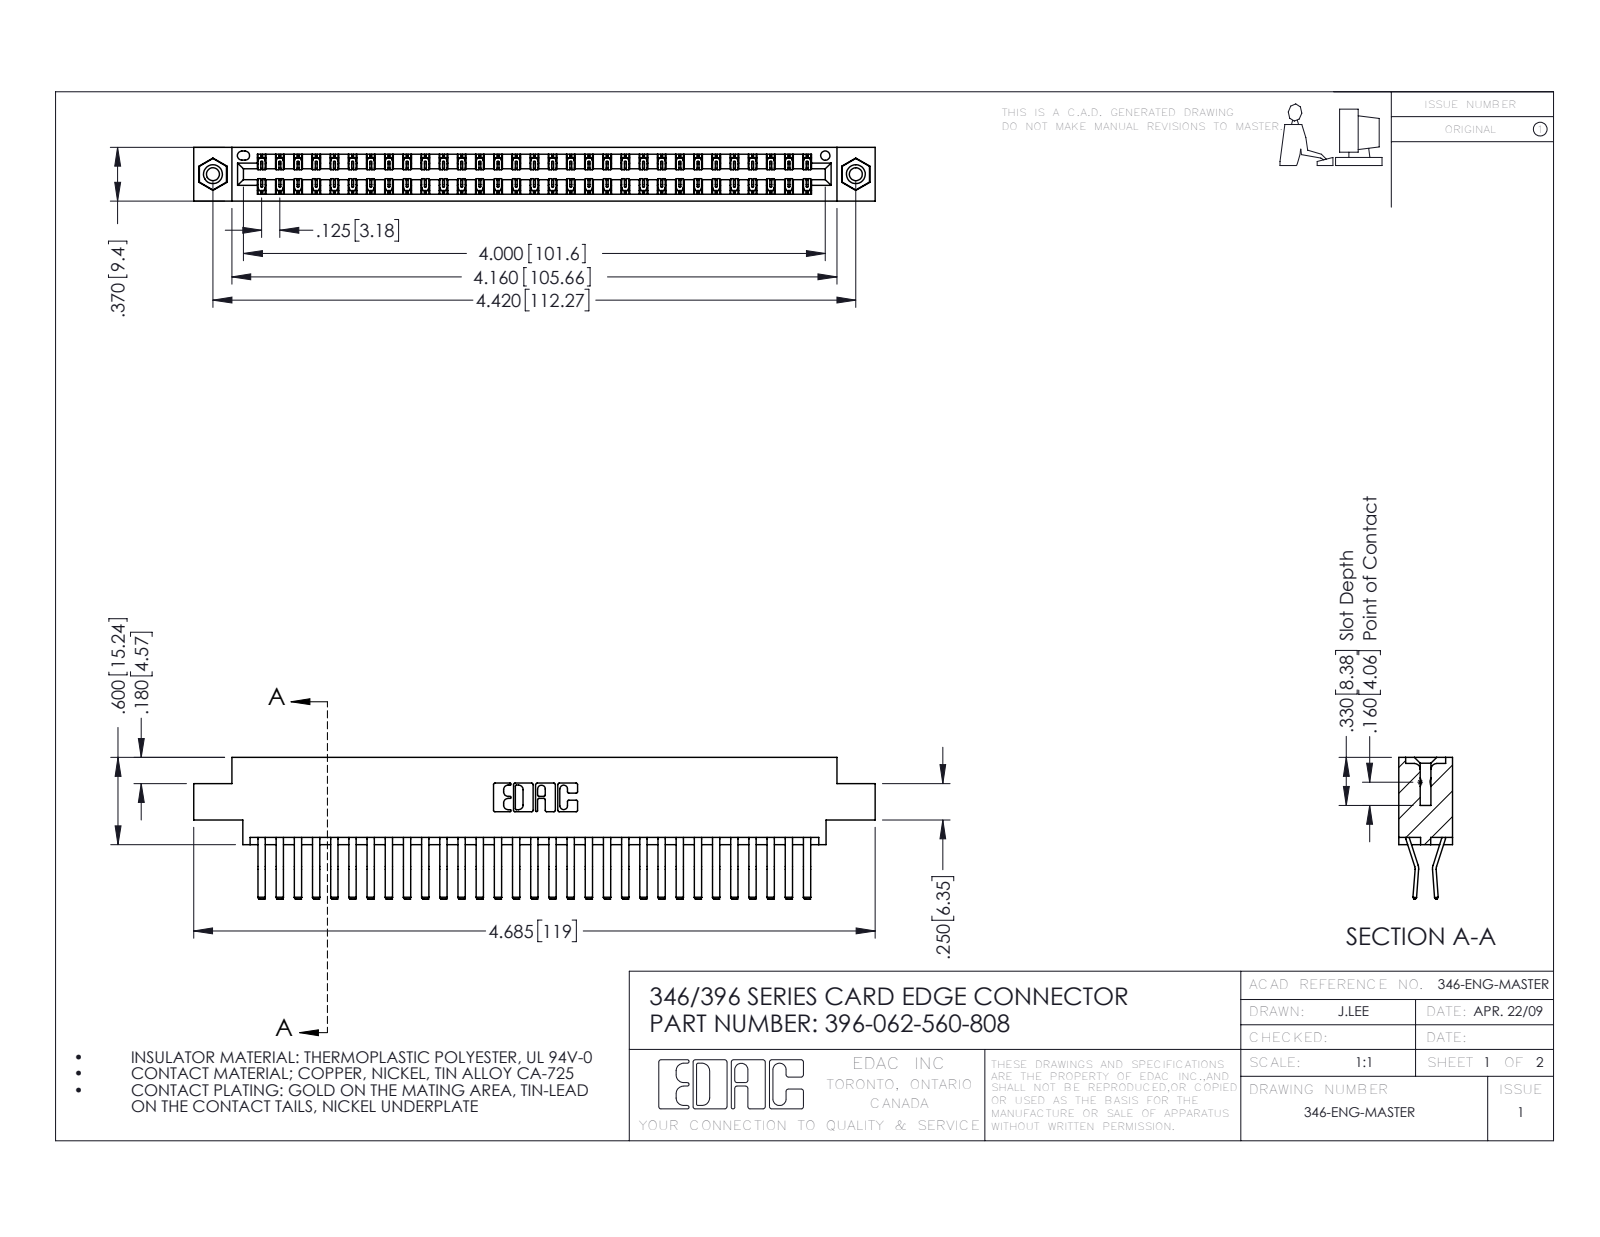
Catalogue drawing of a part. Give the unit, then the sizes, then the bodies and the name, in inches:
Units: inches
Overall size (bounding box): 4.685 × 0.975 × 0.37
Round holes (diameter × count): ⌀0.089 ×2, ⌀0.125 ×2, ⌀0.156 ×2, ⌀0.064 ×1
Round bosses / shafts (diameter × count): ⌀0.155 ×2
Partial cylindrical surfaces — rounded edges, fillets, slot ends (radius × count): R0.006 ×93, R0.01 ×22, R0.007 ×6, R0.031 ×6, R0.026 ×3, R0.01 ×2, R0.014 ×2, R0.022 ×2
Main face-to-face distances: 0.048, 0.322, 0.37, 0.025, 0.25, 0.072, 0.298, 0.275, 0.222, 0.148
Hole centre spacings: 0.246, 4.212, 4.42
Volume: 0.718 in³ · Surface area: 26.79 in²
Bodies: 65 solids, 3534 faces (2282 planar, 1236 cylindrical, 16 other)
Part name (STEP PRODUCT): 345-292-001_560 Tail; 345-250-001_345-250-003-102; 346 Part_0.170 Offset - 0.156 Dia-TI; 396-062-560-808
STEP written by: SolidWorks 2016 (CONFIG_CONTROL_DESIGN)
